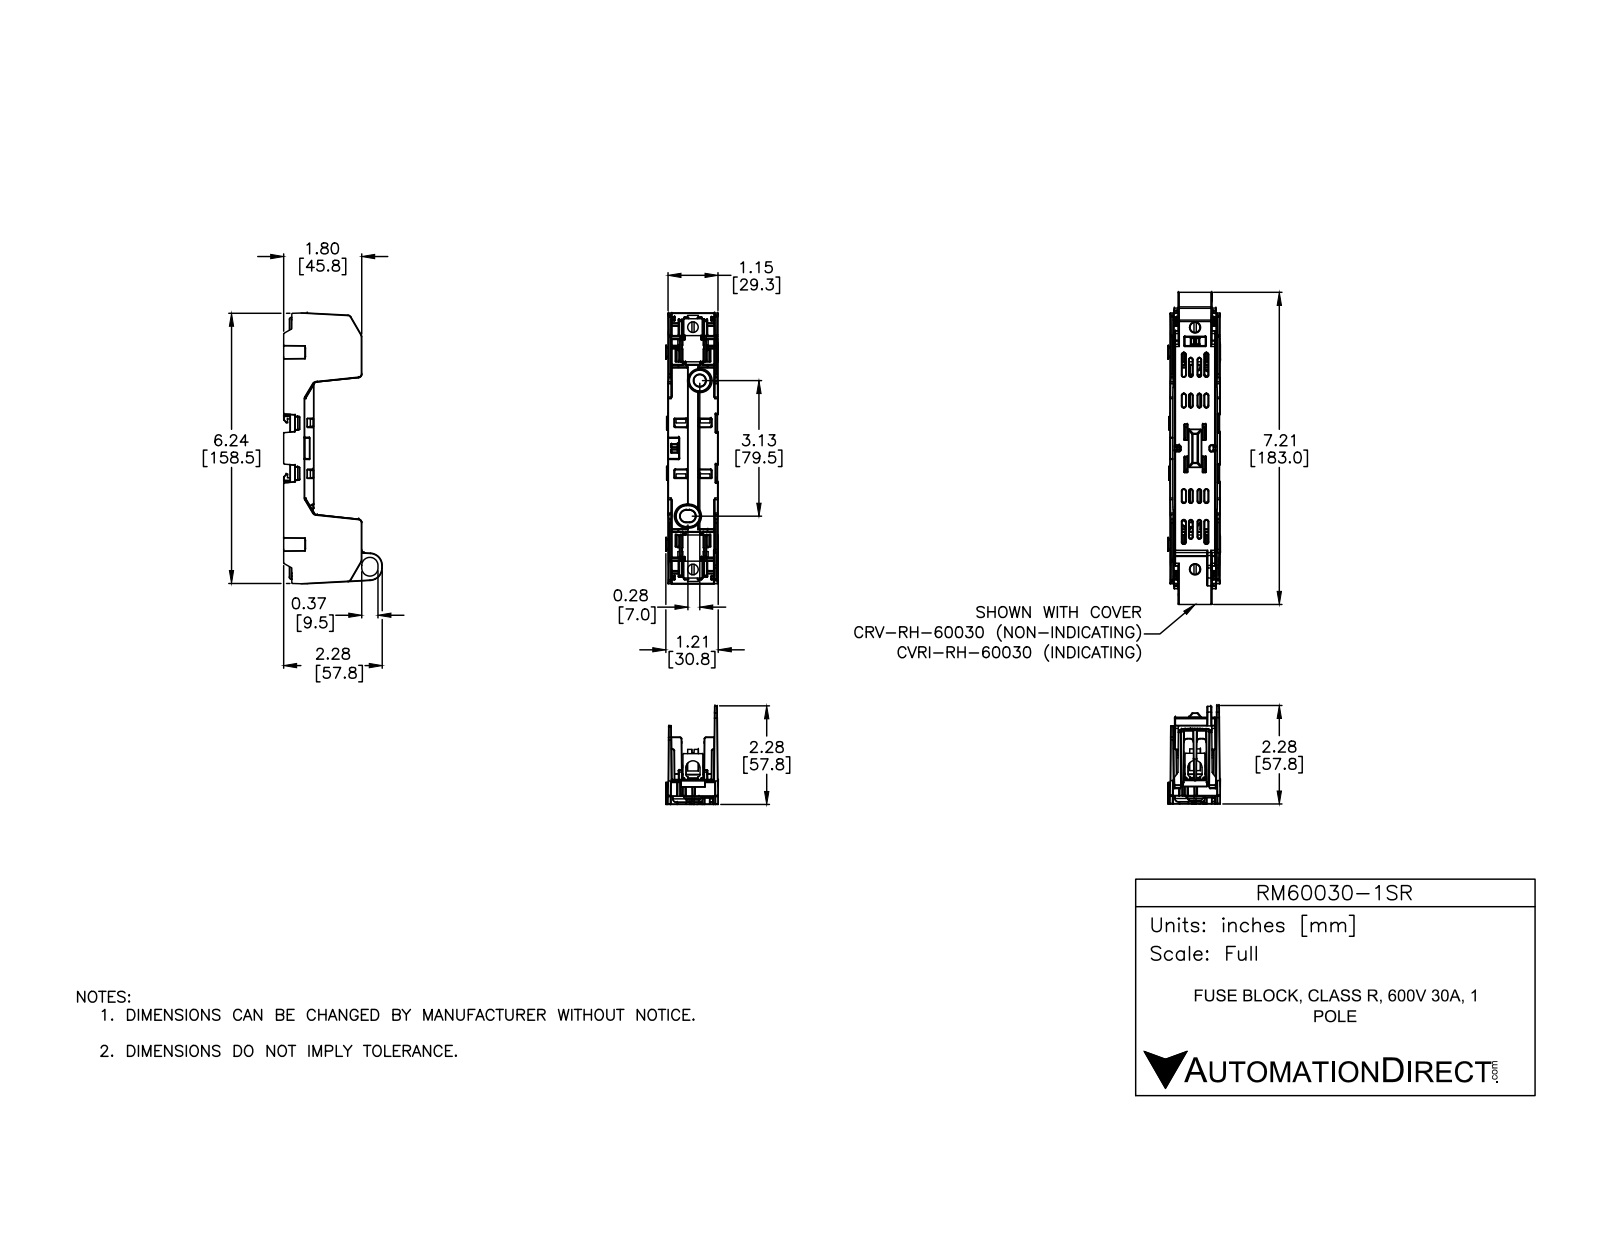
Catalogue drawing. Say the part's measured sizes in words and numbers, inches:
The part is named "RM60030-1SR". Its 3-D file was written by "SolidWorks 2018 (AUTOMOTIVE_DESIGN)". It is 7 solids with 3515 faces: 790 planar, 1473 cylindrical and 1252 other. Overall it measures 6.254 by 2.276 by 1.212 inches. Its volume is 3.184 cubic inches and its surface area 64.18 square inches. Round holes: 2 of diameter 0.244. Round bosses or shafts: 2 of diameter 0.244. Partial cylindrical surfaces (rounded edges, fillets, slot ends): 480 of radius 0.01, 356 of radius 0.006, 69 of radius 0.02, 51 of radius 0.039, 19 of radius 0.079, 16 of radius 0.02, 10 of radius 0.075, 6 of radius 0.059. The main face-to-face distances are 1.067, 0.384, 0.065, 0.187, 0.61, 0.066, 0.457, 1.001, 0.544, 0.122. The hole center spacings are 5.597.
